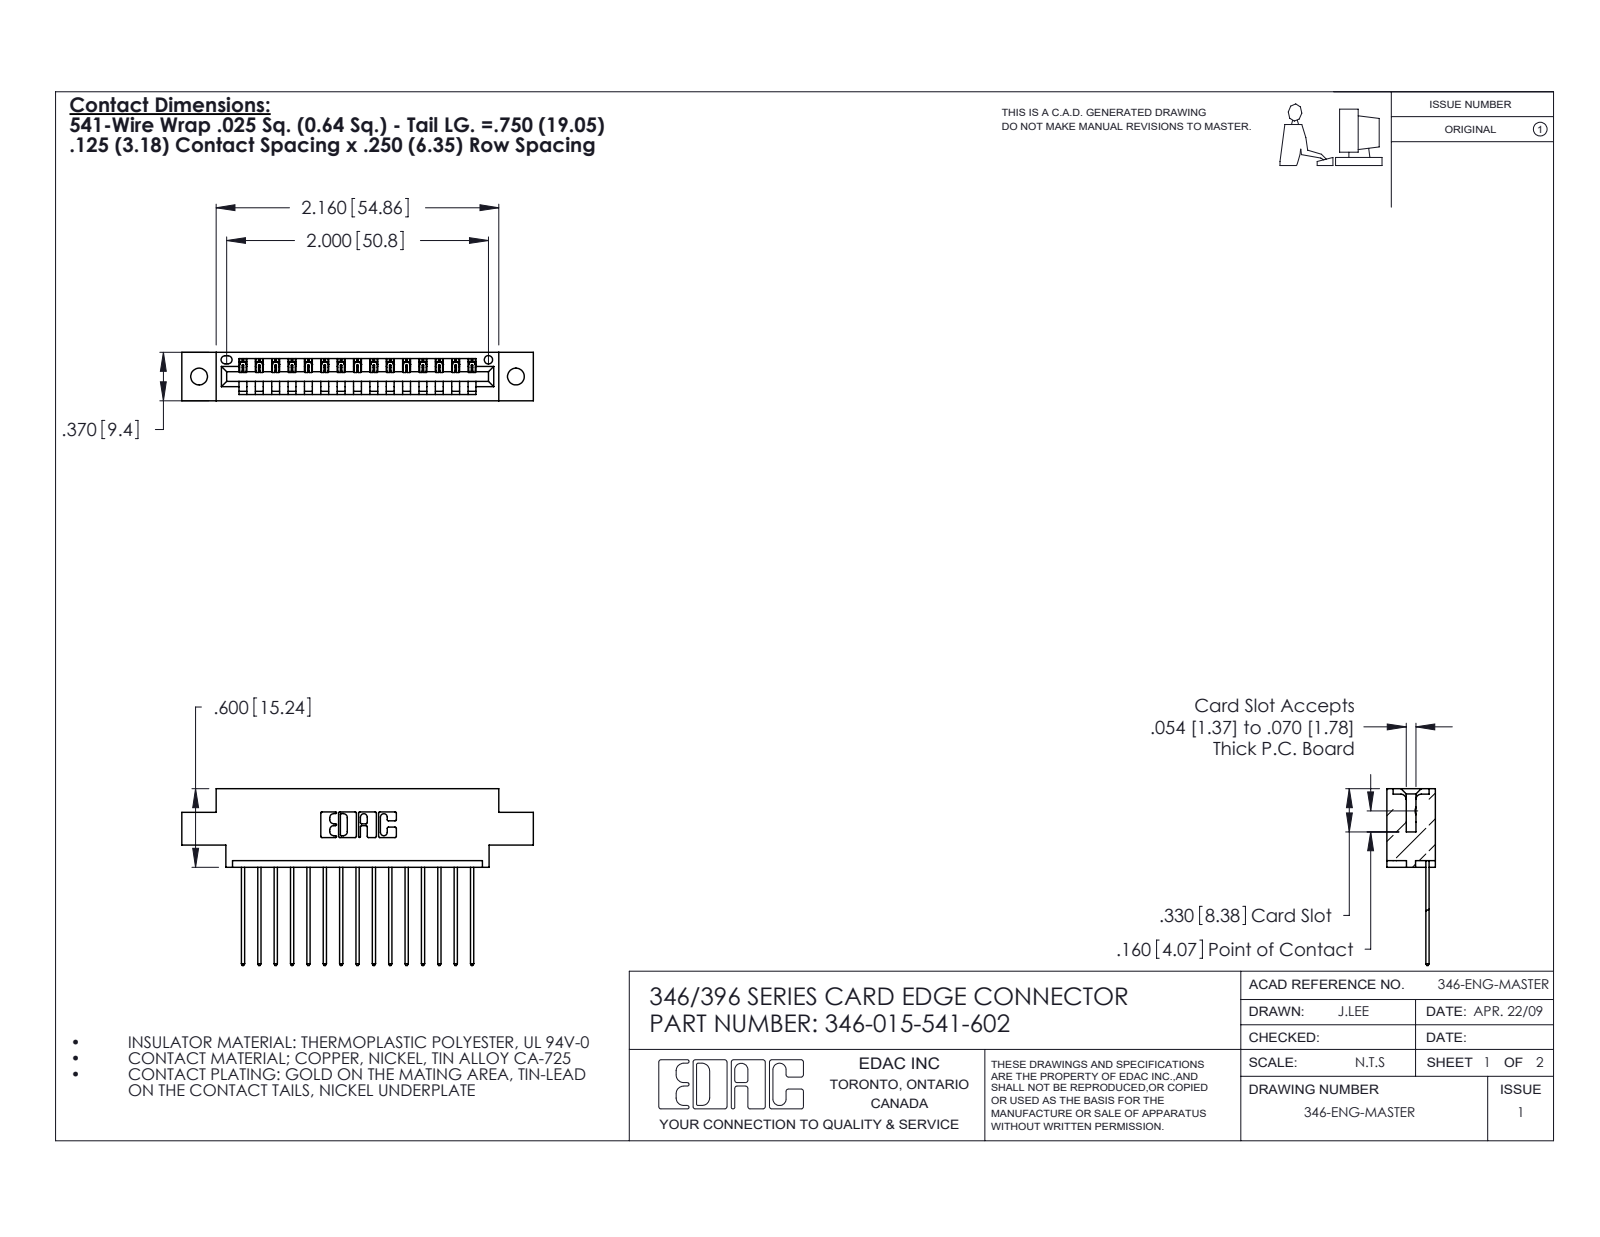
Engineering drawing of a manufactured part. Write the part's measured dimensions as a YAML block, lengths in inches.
part_name: "346-015-541-602; 346 Part_0.170 Offset - 0.128 Dia; 345-292-001_345-293-141"
step_written_by: "SolidWorks 2020 (CONFIG_CONTROL_DESIGN)"
units: inches
bodies: {solids: 16, faces: 996, planar: 680, cylindrical: 316, other: 0}
overall_size: [2.685, 1.35, 0.37]
volume: 0.378
surface_area: 11.85
round_holes:
  - {diameter: 0.128, count: 2}
  - {diameter: 0.064, count: 1}
partial_cylinders:
  - {radius: 0.006, count: 30}
  - {radius: 0.01, count: 30}
  - {radius: 0.01, count: 22}
  - {radius: 0.007, count: 6}
  - {radius: 0.031, count: 6}
  - {radius: 0.026, count: 3}
  - {radius: 0.031, count: 2}
  - {radius: 0.04, count: 2}
face_to_face_distances: [0.048, 0.322, 0.37, 0.25, 0.072, 0.298, 0.025, 0.148, 0.222, 0.1]
hole_center_spacings: [0.246, 2.213, 2.42]
